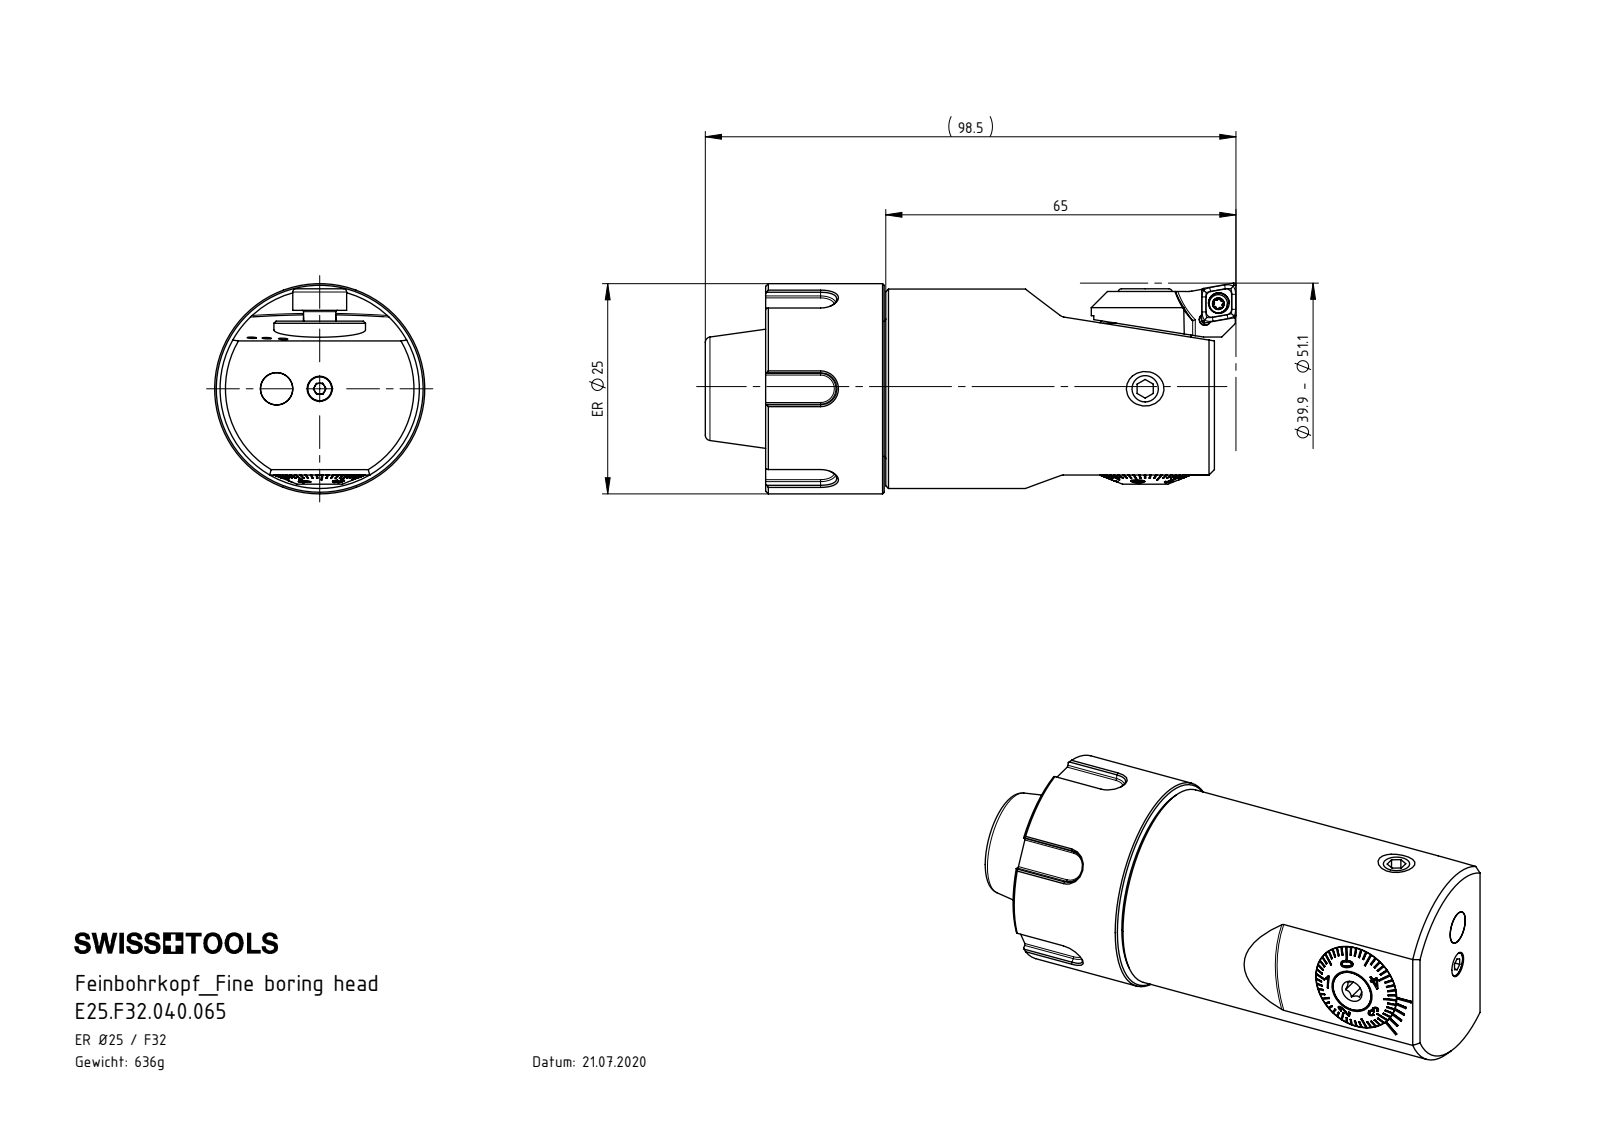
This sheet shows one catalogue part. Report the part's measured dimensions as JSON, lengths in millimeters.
{"part_name": "MSX-ER1.XXX.XXX_A_Mutter Spannzangenkegel E25; F32-BG2.017.004_A; T7 M2.5 x 6; ISO 4026 - M6 x 8 (+8 more)", "step_written_by": "SolidWorks 2017 (AUTOMOTIVE_DESIGN)", "units": "millimeters", "bodies": {"solids": 16, "faces": 617, "planar": 344, "cylindrical": 80, "other": 193}, "overall_size": [94.5, 39, 39], "volume_mm3": 81830, "surface_area_mm2": 28155, "round_holes": [[1.5, 3], [3.3, 2], [5, 2], [2.05, 1], [2.7, 1], [2.9, 1], [3, 1], [4.2, 1], [6, 1], [6.8, 1], [7, 1], [7.4, 1]], "round_bosses_or_shafts": [[6, 2], [39, 1], [37, 1], [25, 1], [23, 1], [17, 1], [16.98, 1], [16.85, 1]], "partial_cylinders_radius": [[0.3, 12], [1.4, 4], [0.5, 3], [1.75, 2], [2, 2], [3.2, 1]], "face_to_face_distances": [61.3, 61, 2.2, 3.7, 4.5, 22, 22.3, 83.3, 0.8, 5.9], "hole_center_spacings": [8, 8.72]}
